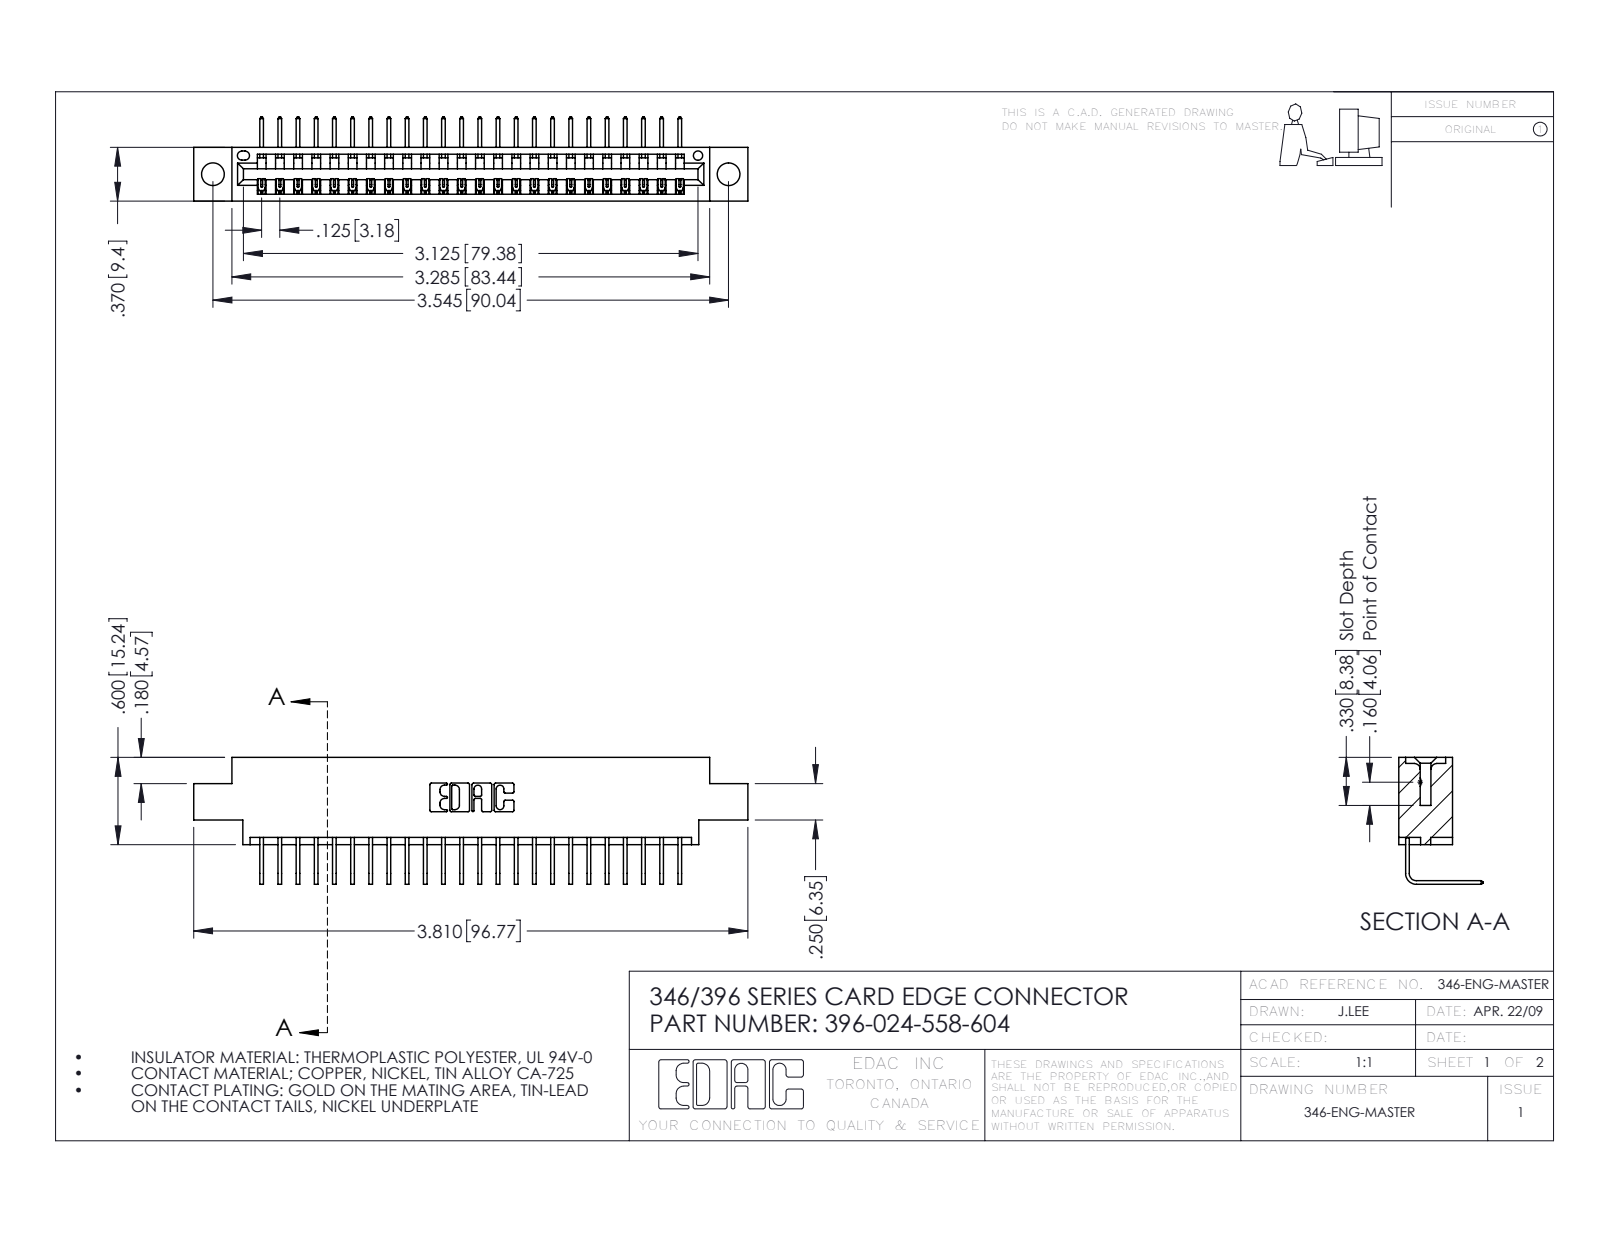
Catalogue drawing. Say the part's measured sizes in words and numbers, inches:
The part is named "346 Part_0.170 Offset - 0.156 Dia-TH; 345-292-001_558 Tail - 2; 396-024-558-604". Its 3-D file was written by "SolidWorks 2016 (CONFIG_CONTROL_DESIGN)". It is 25 solids with 1566 faces: 1088 planar, 478 cylindrical and 0 other. Overall it measures 3.81 by 0.873 by 0.58 inches. Its volume is 0.548 cubic inches and its surface area 17.78 square inches. Round holes: 2 of diameter 0.156, 1 of diameter 0.064. Partial cylindrical surfaces (rounded edges, fillets, slot ends): 48 of radius 0.006, 22 of radius 0.01, 6 of radius 0.007, 6 of radius 0.031, 3 of radius 0.026, 2 of radius 0.031, 2 of radius 0.04, 1 of radius 0.014. The main face-to-face distances are 0.322, 0.048, 0.37, 0.25, 0.298, 0.025, 0.072, 0.148, 0.222, 0.1. The hole center spacings are 0.246, 3.337, 3.545.
